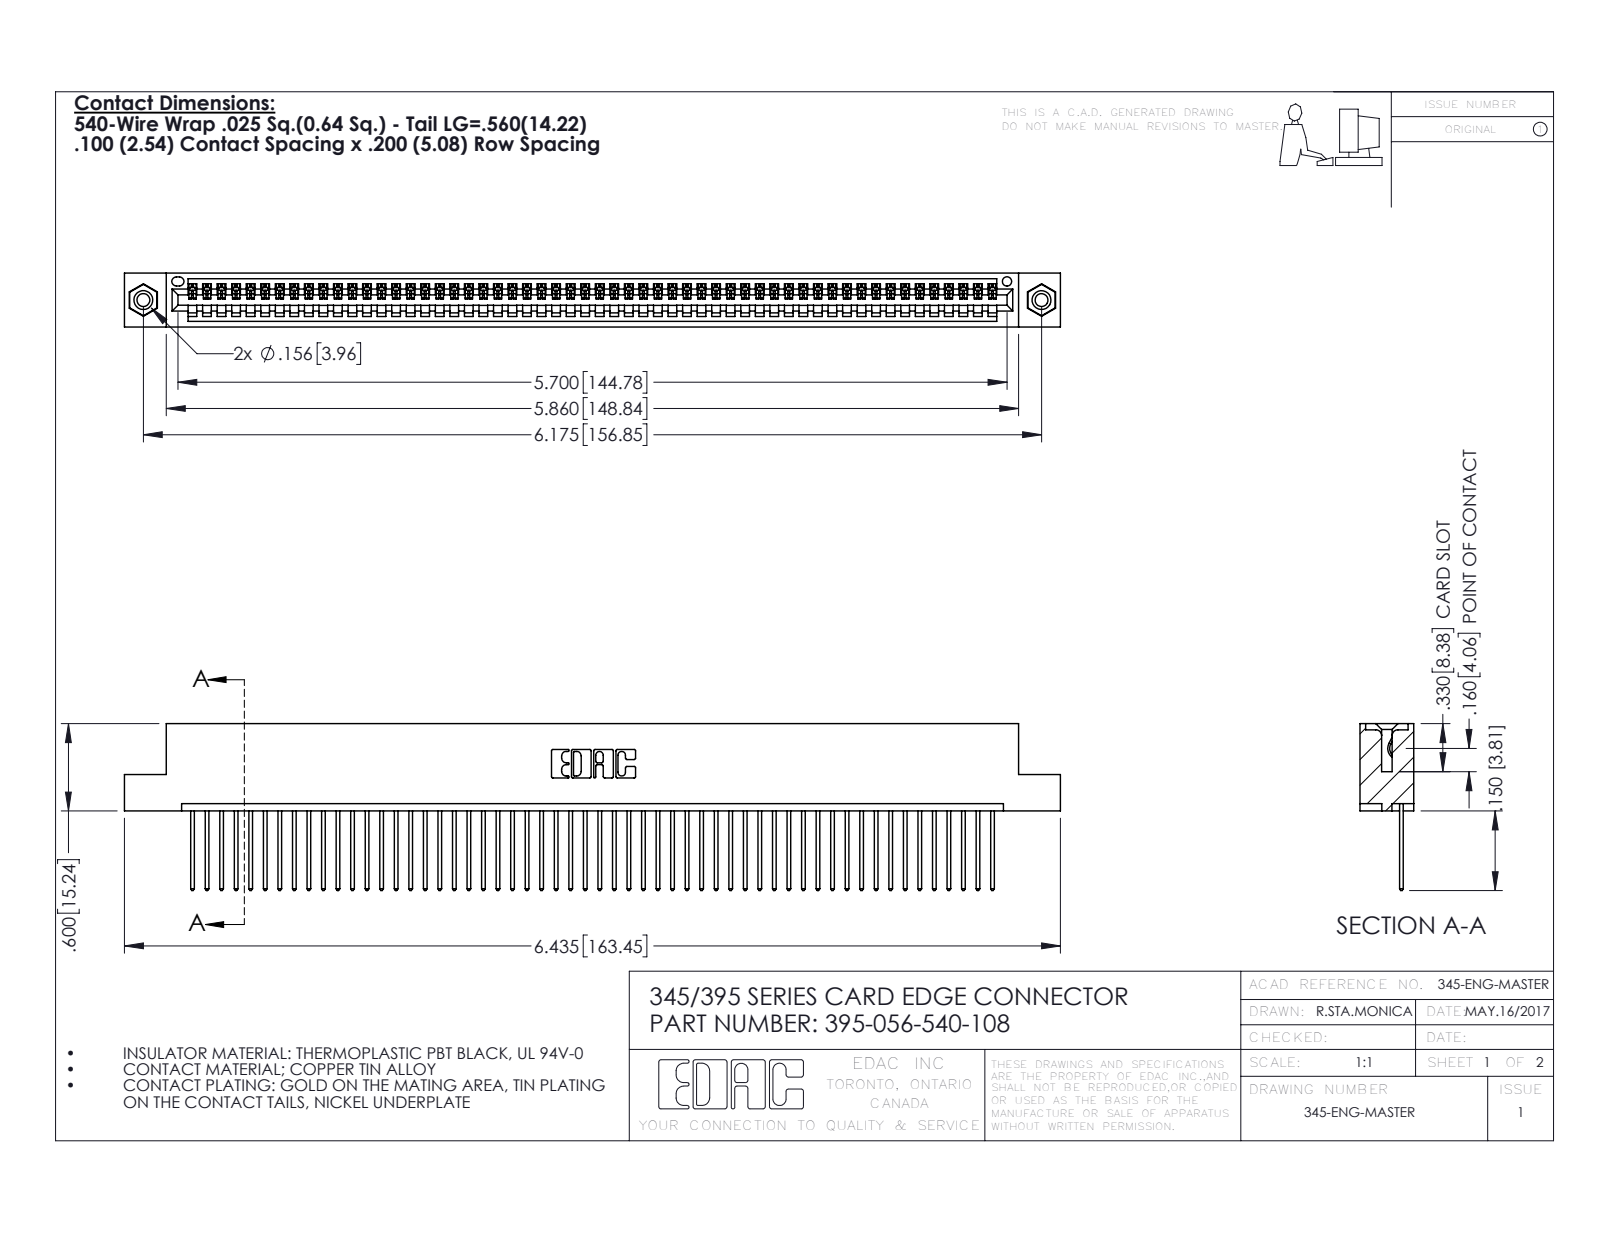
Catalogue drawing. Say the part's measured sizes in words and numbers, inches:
The part is named "345-250-001_345-250-003-102; 345-292-001_345-293-140; 345 Part_Flush Mounting Lugs - 0.156 Dia-TI; 395-056-540-108". Its 3-D file was written by "SolidWorks 2016 (CONFIG_CONTROL_DESIGN)". It is 59 solids with 3434 faces: 2352 planar, 1066 cylindrical and 16 other. Overall it measures 6.435 by 1.147 by 0.37 inches. Its volume is 0.959 cubic inches and its surface area 33.53 square inches. Round holes: 2 of diameter 0.089, 2 of diameter 0.125, 2 of diameter 0.156, 1 of diameter 0.064. Round bosses or shafts: 2 of diameter 0.155. Partial cylindrical surfaces (rounded edges, fillets, slot ends): 112 of radius 0.006, 112 of radius 0.01, 22 of radius 0.01, 6 of radius 0.007, 6 of radius 0.031, 3 of radius 0.026, 2 of radius 0.031, 2 of radius 0.04. The main face-to-face distances are 0.072, 0.298, 0.37, 0.098, 0.272, 0.025, 0.2, 0.225, 0.149, 0.072. The hole center spacings are 0.27, 5.939, 6.175.
